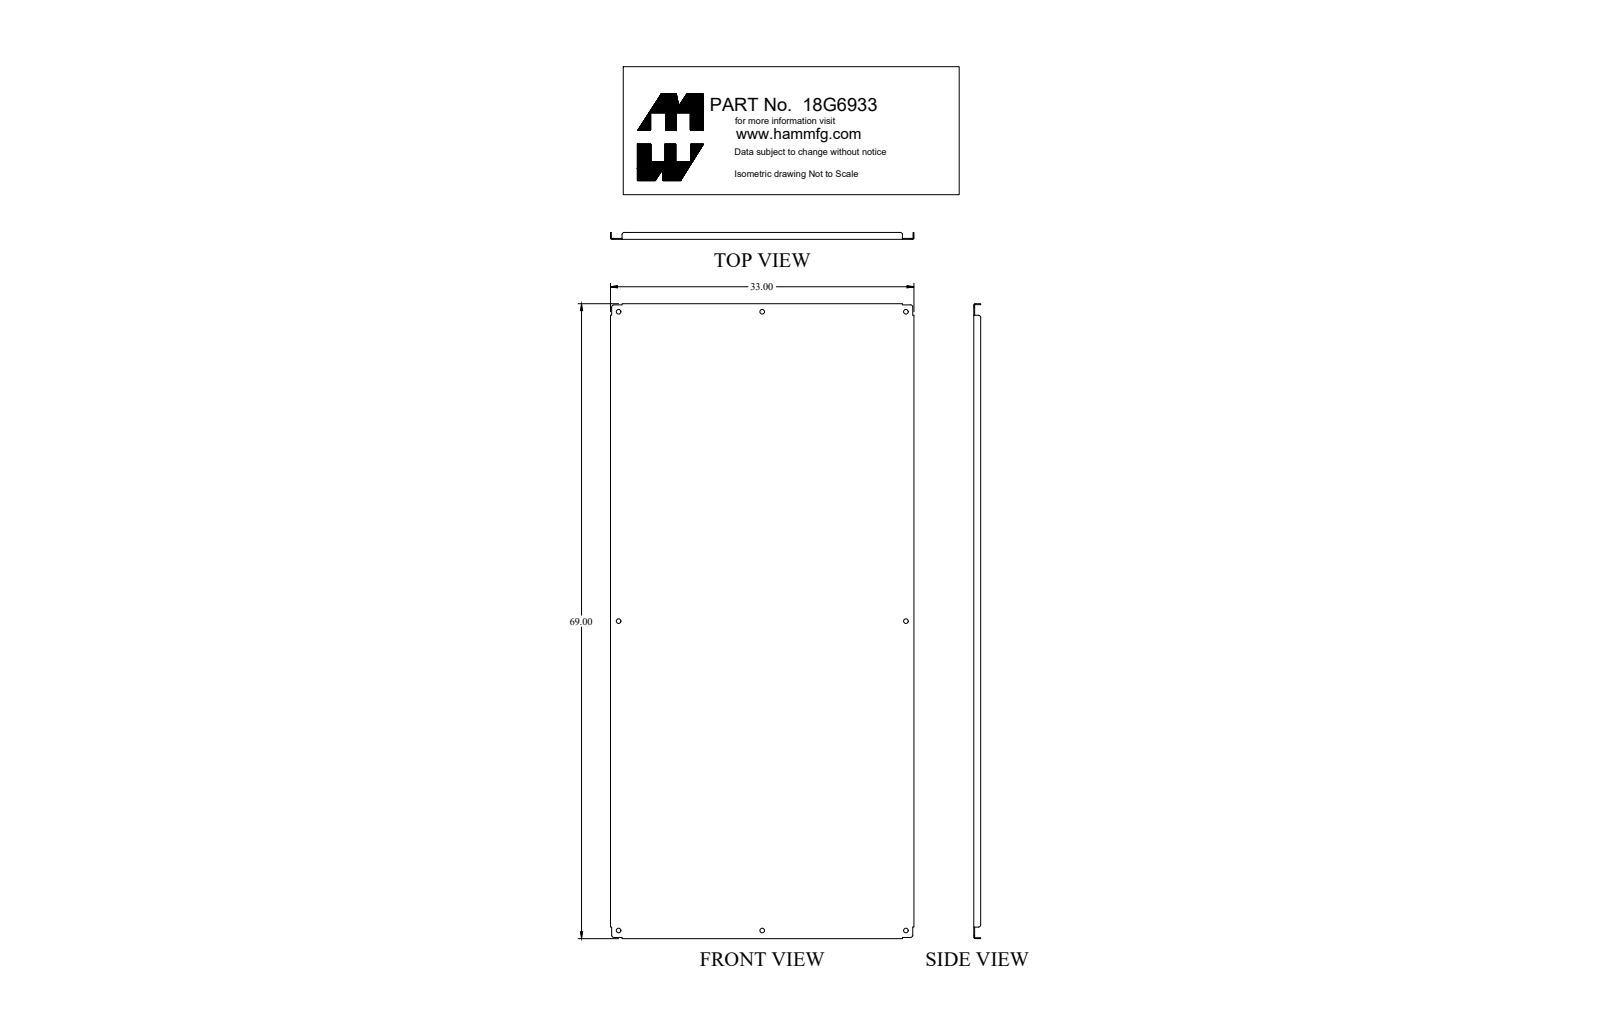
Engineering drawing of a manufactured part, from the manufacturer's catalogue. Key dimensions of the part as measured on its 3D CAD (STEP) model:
Part name (STEP PRODUCT): 18G6933_Default
STEP written by: SolidWorks 2018 (CONFIG_CONTROL_DESIGN)
Units: inches
Bodies: 1 solid, 66 faces (30 planar, 36 cylindrical, 0 other)
Overall size (bounding box): 69 × 33 × 0.75
Volume: 227.5 in³ · Surface area: 4 810 in²
Round holes (diameter × count): ⌀0.5 ×8
Partial cylindrical surfaces — rounded edges, fillets, slot ends (radius × count): R0.25 ×8, R0.03 ×4, R0.125 ×4
Main face-to-face distances: 0.095, 32.905, 32.81, 33, 68.905, 69, 68.81, 0.75, 0.655, 0.125
Hole centre spacings: 15.625, 33.625, 37.078, 45.904, 69.041, 31.25, 67.25, 74.156
